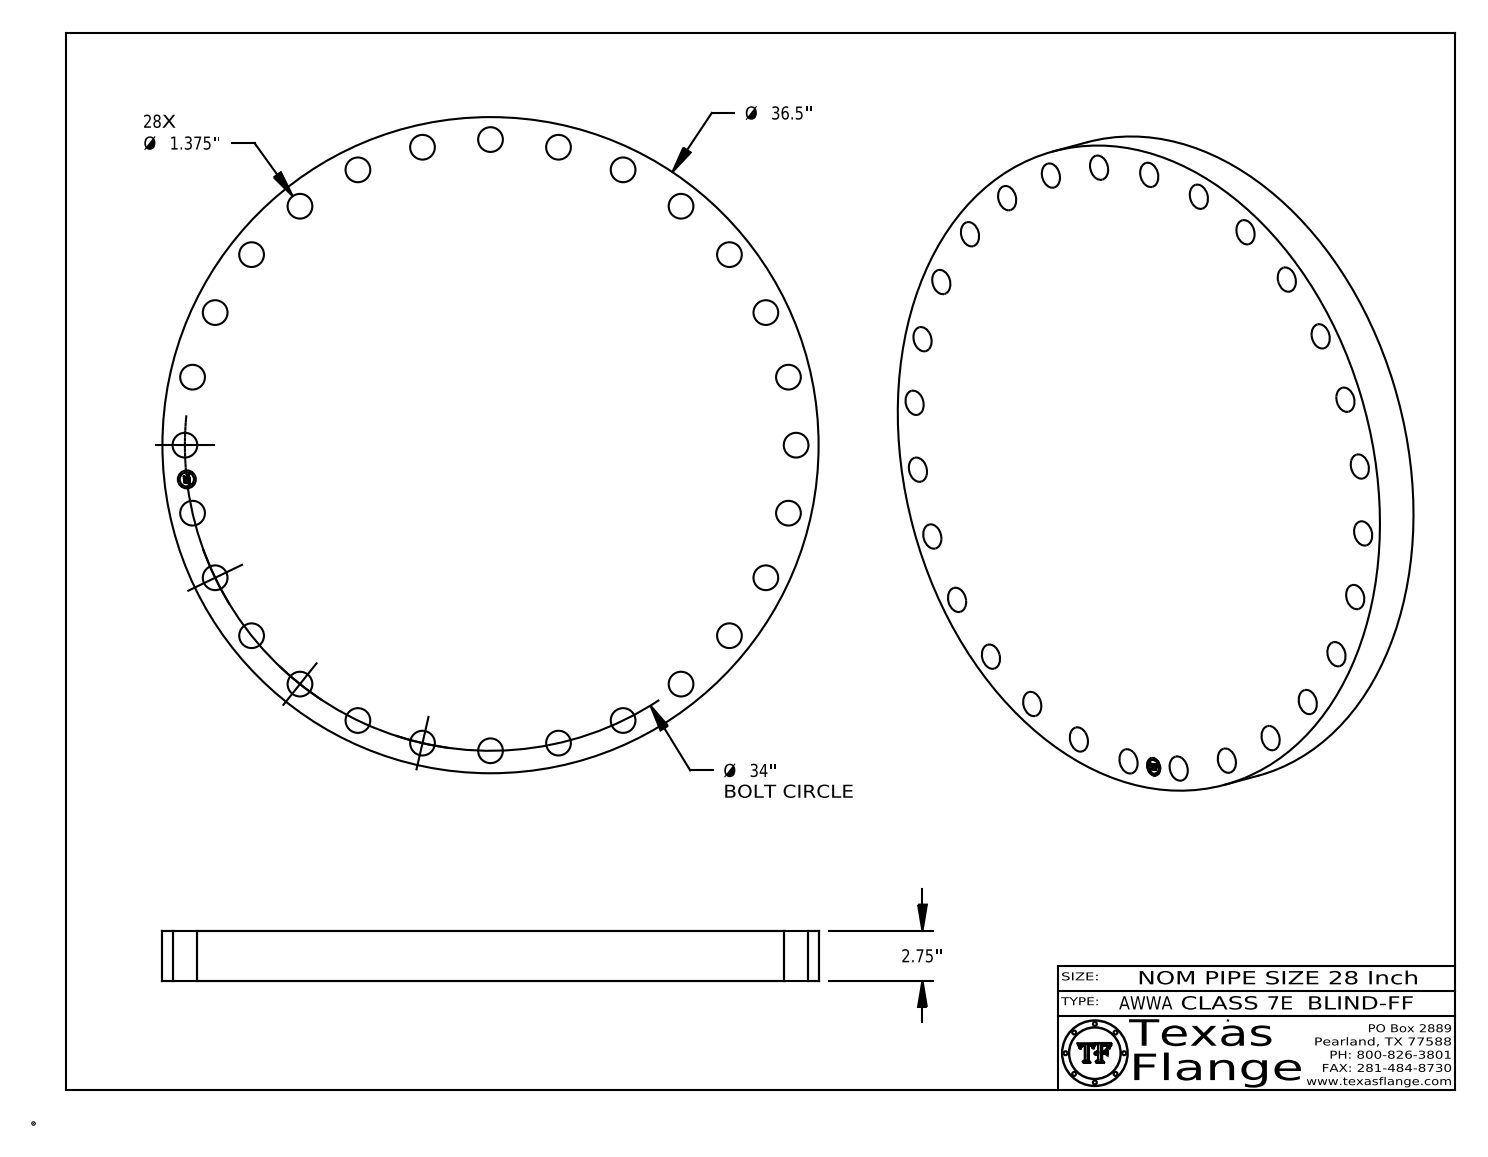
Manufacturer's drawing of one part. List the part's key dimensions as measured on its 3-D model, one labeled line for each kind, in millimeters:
Part name (STEP PRODUCT): AWWA Class 7E-BLIND-FF
STEP written by: CATIA V5 STEP AP214 (AUTOMOTIVE_DESIGN)
Units: millimetres
Bodies: 1 solid, 445 faces (367 planar, 78 cylindrical, 0 other)
Overall size (bounding box): 927.1 × 927.1 × 69.9
Volume: 45 280 000 mm³ · Surface area: 1 715 000 mm²
Round holes (diameter × count): ⌀34.9 ×28, ⌀25.4 ×1
Round bosses / shafts (diameter × count): ⌀1.5 ×8, ⌀927.1 ×1, ⌀20 ×1
Main face-to-face distances: 69.9, 0.4, 69.5, 7.6, 7.4, 1.4, 4.9, 6.3, 1.1, 3.8
Hole centre spacings: 96.7, 192.2, 778.1, 858.2, 285.2, 459.5, 538.4, 841.9
